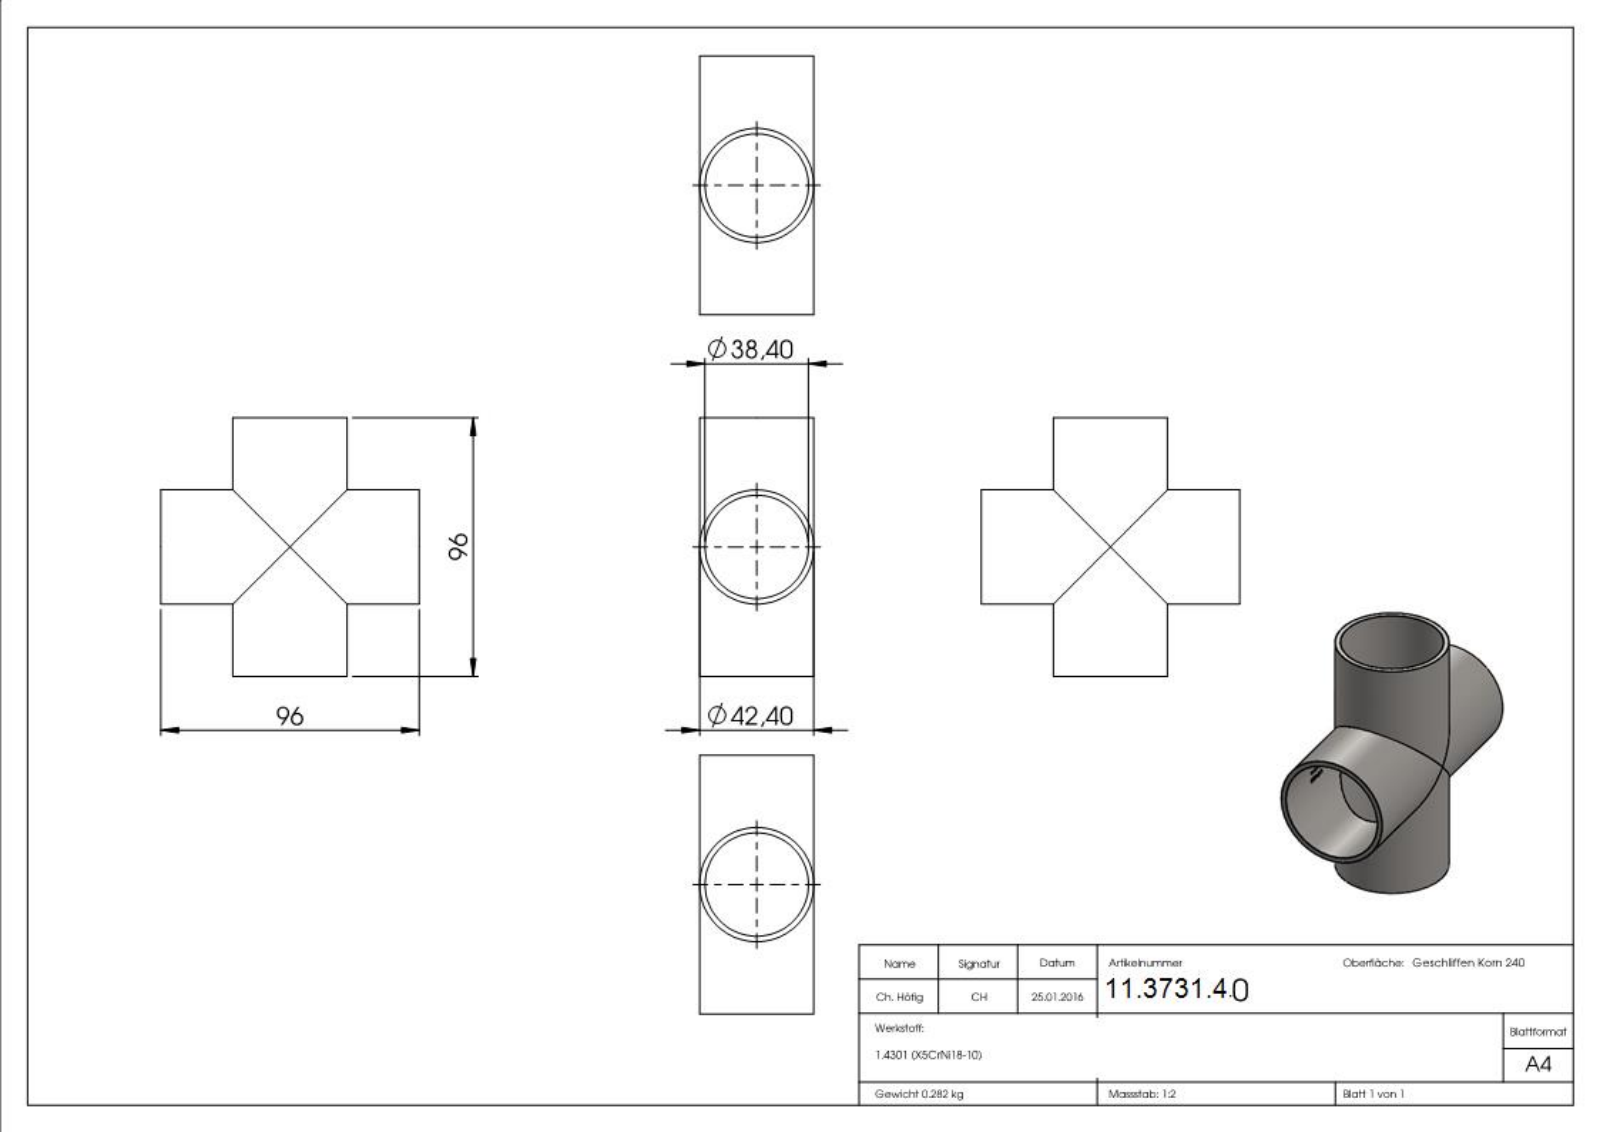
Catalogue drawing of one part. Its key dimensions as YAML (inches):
part_name: "55171-240"
step_written_by: "SolidWorks 2015 (CONFIG_CONTROL_DESIGN)"
units: inches
bodies: {solids: 1, faces: 237, planar: 111, cylindrical: 47, other: 79}
overall_size: [3.78, 3.78, 1.669]
volume: 2.177
surface_area: 56.84
round_holes:
  - {diameter: 1.512, count: 2}
round_bosses_or_shafts:
  - {diameter: 1.669, count: 2}
partial_cylinders:
  - {radius: 0.76, count: 1}
face_to_face_distances: [3.78, 0.015, 0.05, 0.126, 0.08, 1.89, 0.08, 0.174, 0.113, 0.052]
